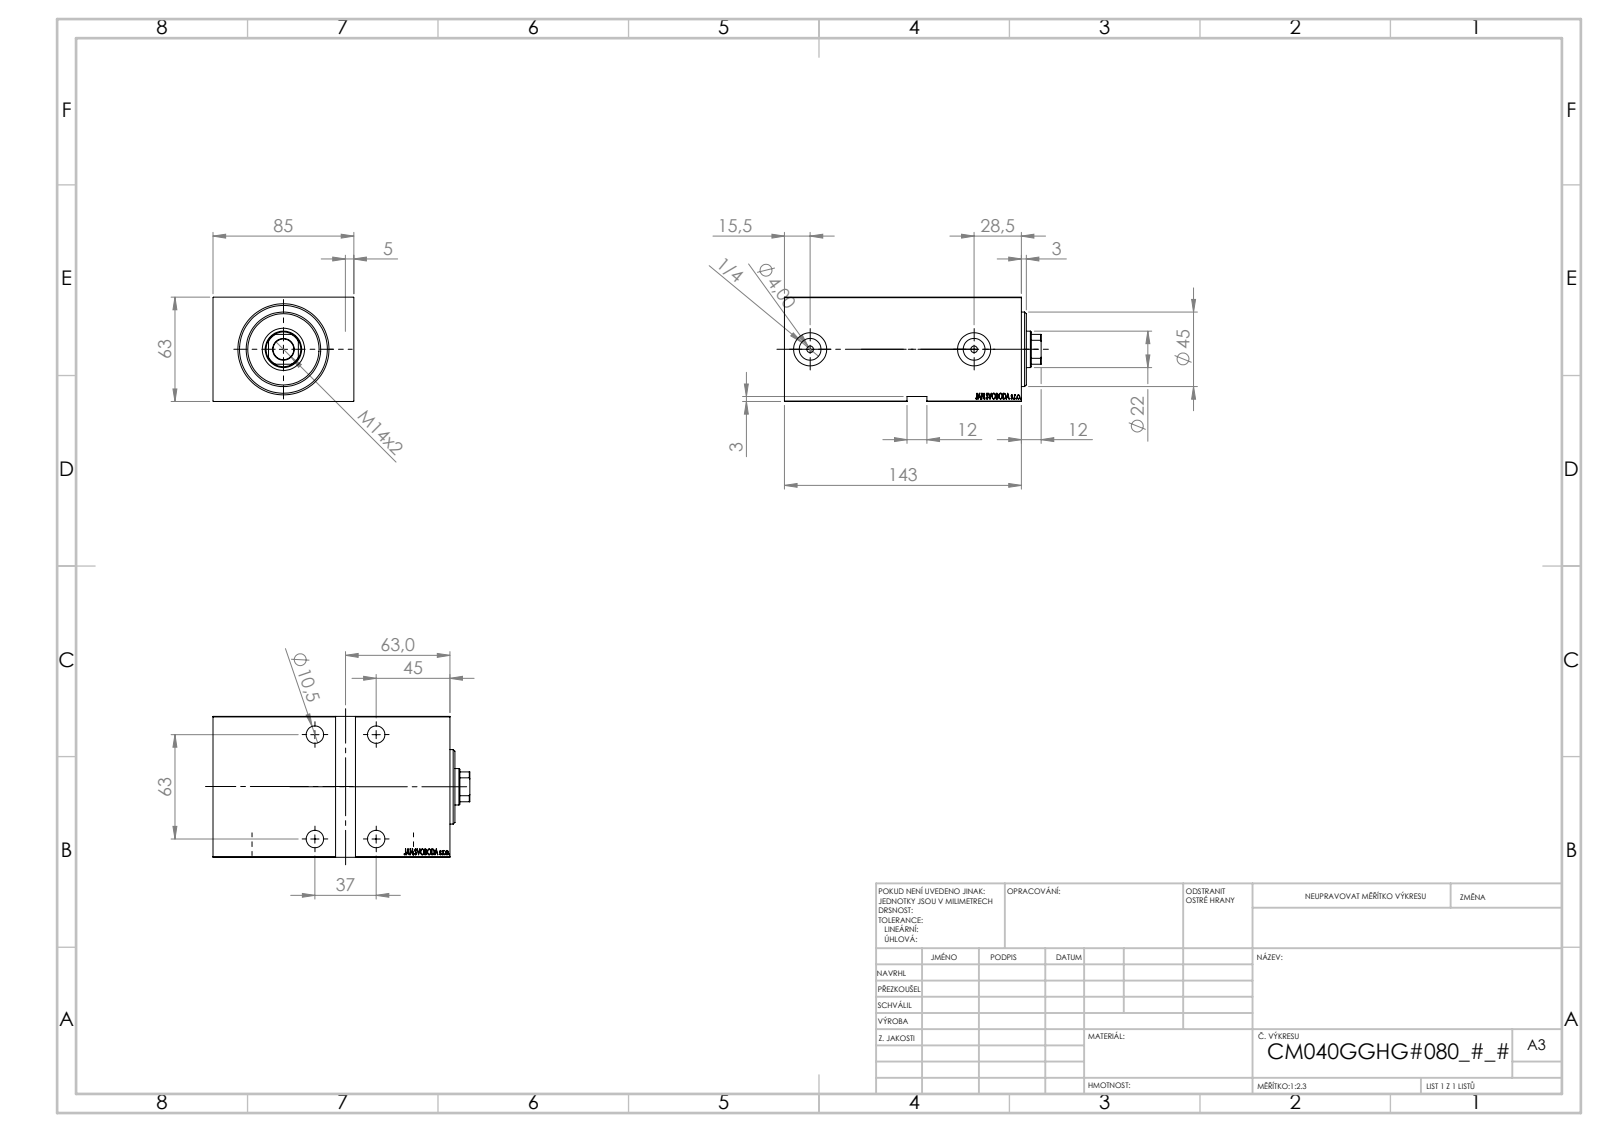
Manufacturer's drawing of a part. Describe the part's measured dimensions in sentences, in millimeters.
The part is named "V450CM_G_VCP; V450CM_VC_G; Zatka_OIL_PORT; V450CM_G_Body". Its 3-D file was written by "SolidWorks 2019 (CONFIG_CONTROL_DESIGN)". It is 5 solids with 897 faces: 441 planar, 58 cylindrical and 398 other. Overall it measures 155 by 85 by 63 millimeters. Its volume is 659 854 cubic millimeters and its surface area 103 751 square millimeters. Round holes: 4 of diameter 10.5, 4 of diameter 16.5, 2 of diameter 4, 2 of diameter 13.16, 2 of diameter 20, 1 of diameter 12.5, 1 of diameter 22, 1 of diameter 25.5, 1 of diameter 40, 1 of diameter 42, 1 of diameter 53. Round bosses or shafts: 2 of diameter 18, 1 of diameter 45, 1 of diameter 27. Partial cylindrical surfaces (rounded edges, fillets, slot ends): 1 of radius 10.5. The main face-to-face distances are 63, 85, 143, 12, 131, 5, 138, 126, 3, 60. The hole center spacings are 37, 63, 73.06, 99.
